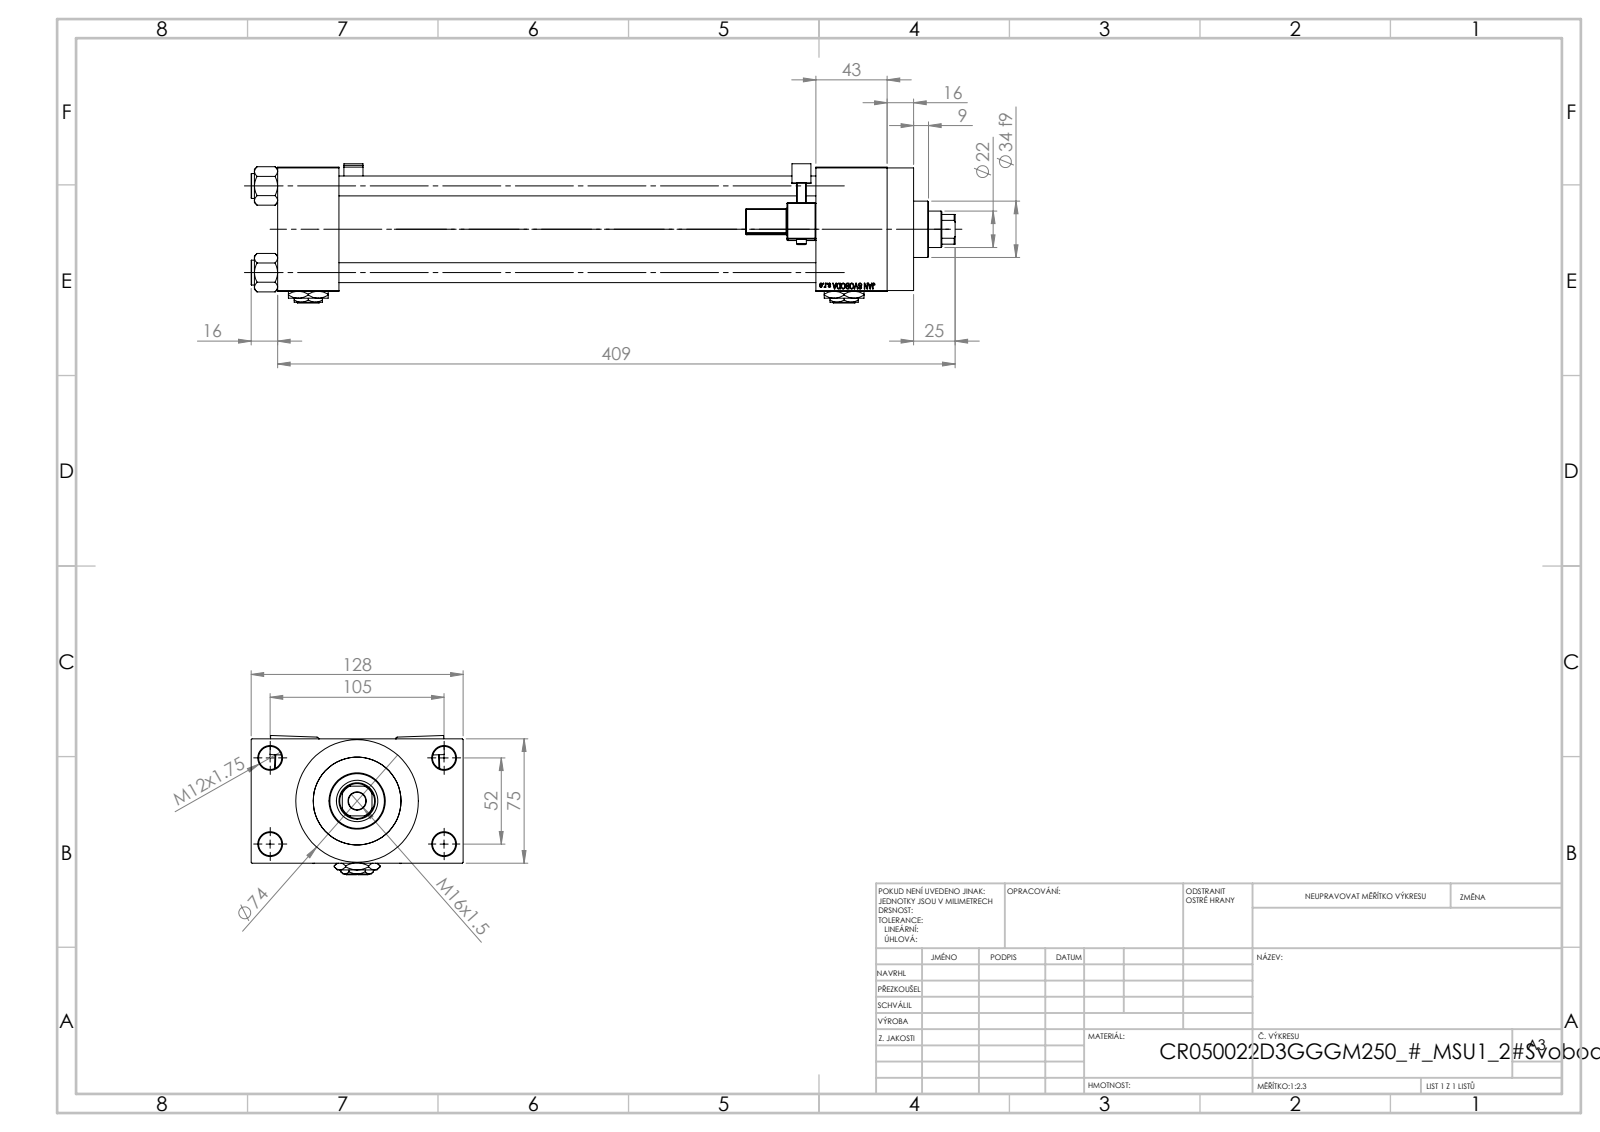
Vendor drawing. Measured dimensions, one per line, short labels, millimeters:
name: V215CR_VCP_D; Zatka_pro_OIL_PORT; V215_VC_A; NUT_M5_D (+3 more)
written by: SolidWorks 2019 (CONFIG_CONTROL_DESIGN)
unit: mm
bodies: 15 solids, 1359 faces (603 planar, 160 cylindrical, 596 other)
size: 425 × 128 × 84.03
volume: 1 150 000 mm³; area: 308 624 mm²
holes: 4× ⌀12, 4× ⌀14, 2× ⌀7, 2× ⌀20.96, 2× ⌀30, 1× ⌀10.5, 1× ⌀22, 1× ⌀25, 1× ⌀41, 1× ⌀50, 1× ⌀53
bosses: 4× ⌀15, 2× ⌀6, 1× ⌀74, 1× ⌀56, 1× ⌀34
rounds: 48× R0.5, 2× R1, 2× R2.5, 2× R4, 1× R10.5
face distances: 75, 288, 101.5, 37, 325, 26.5, 368, 331, 43, 16
hole spacings: 26.35, 36.98, 52.3, 58.43, 58.59, 78.65, 94.37, 52
